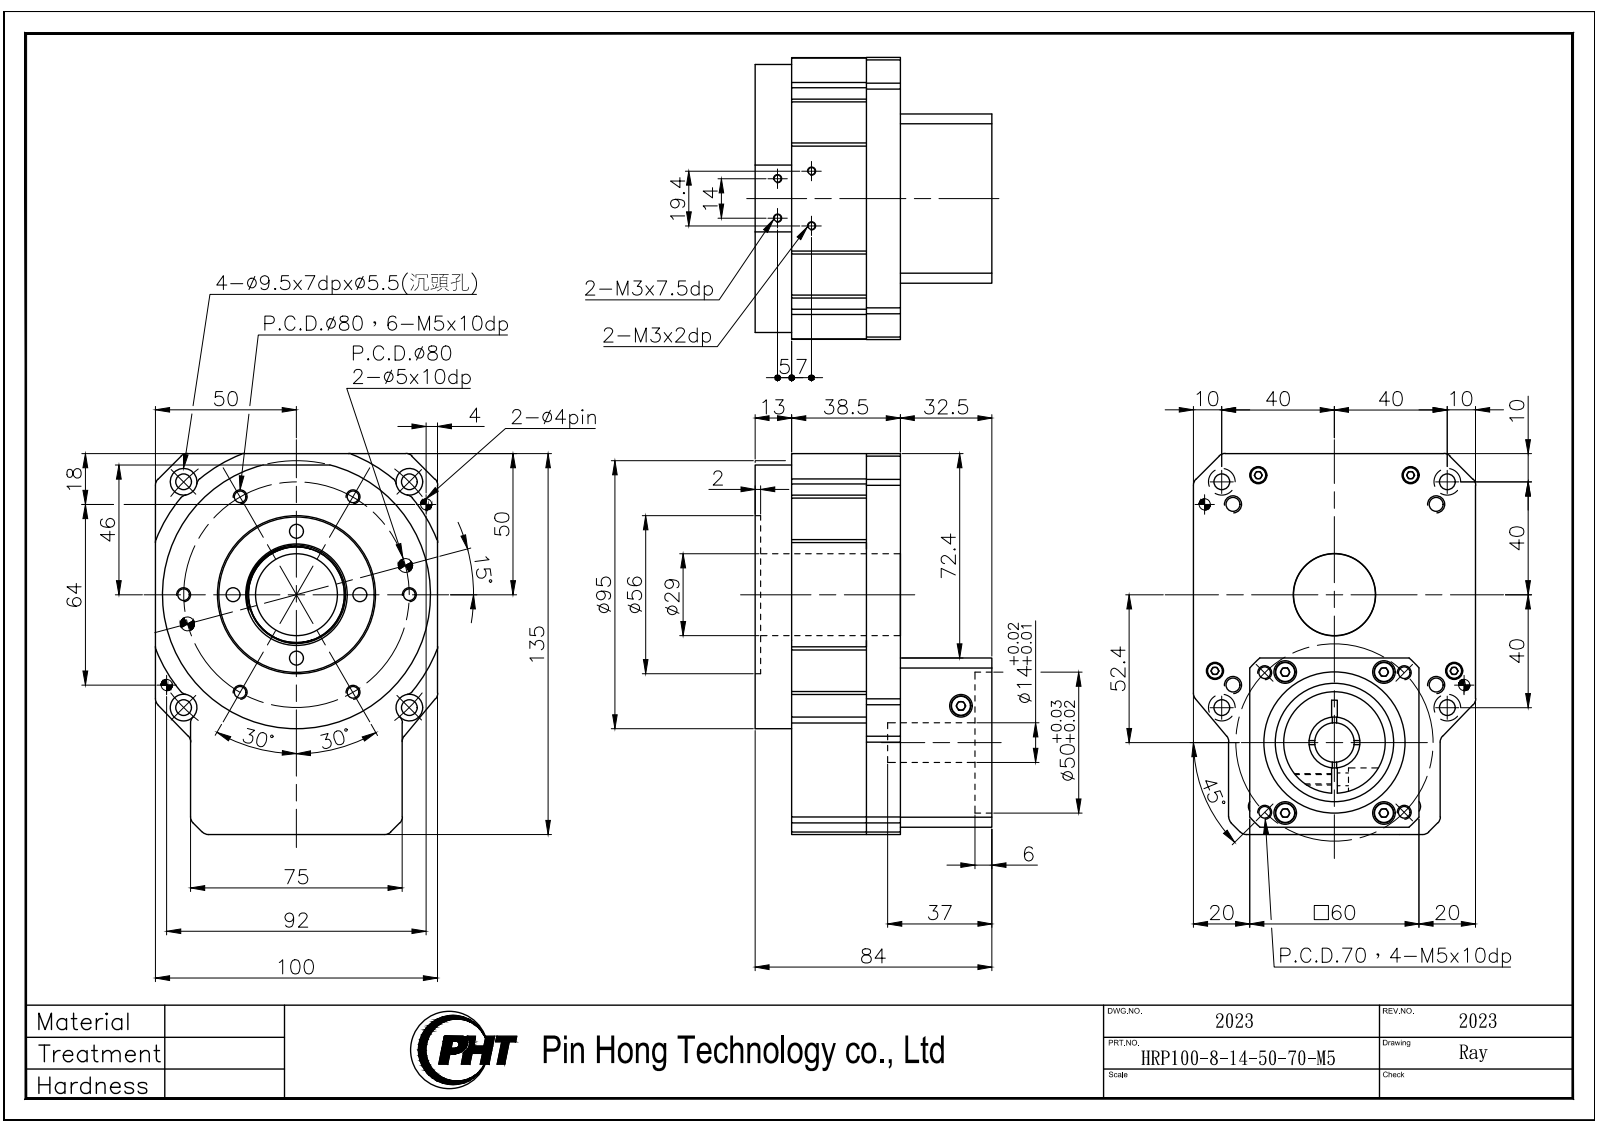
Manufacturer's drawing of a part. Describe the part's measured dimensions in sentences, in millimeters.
The part is named "HRP100-8-14-50-70-M5_2023". Its 3-D file was written by "SolidWorks 2016 (CONFIG_CONTROL_DESIGN)". It is 1 solid with 409 faces: 162 planar, 195 cylindrical and 52 other. Overall it measures 135 by 100 by 84 millimeters. Its volume is 581 393 cubic millimeters and its surface area 74 798 square millimeters. Round holes: 10 of diameter 4.2, 10 of diameter 5, 6 of diameter 8, 5 of diameter 4.5, 4 of diameter 2.5, 4 of diameter 3.4, 4 of diameter 5.5, 4 of diameter 6, 4 of diameter 9.5, 2 of diameter 4, 1 of diameter 3.3, 1 of diameter 14. Round bosses or shafts: 4 of diameter 7, 4 of diameter 5.5, 1 of diameter 95, 1 of diameter 55, 1 of diameter 36, 1 of diameter 20, 1 of diameter 18. Partial cylindrical surfaces (rounded edges, fillets, slot ends): 30 of radius 3, 4 of radius 4.8, 1 of radius 3.9, 1 of radius 40, 1 of radius 53.5. The main face-to-face distances are 38.5, 51.5, 60, 13, 12.5, 87.45, 19.95, 79.95, 20, 80. The hole center spacings are 43.66, 74.2, 80, 7.26, 8.94, 10, 13.22, 22.5.
